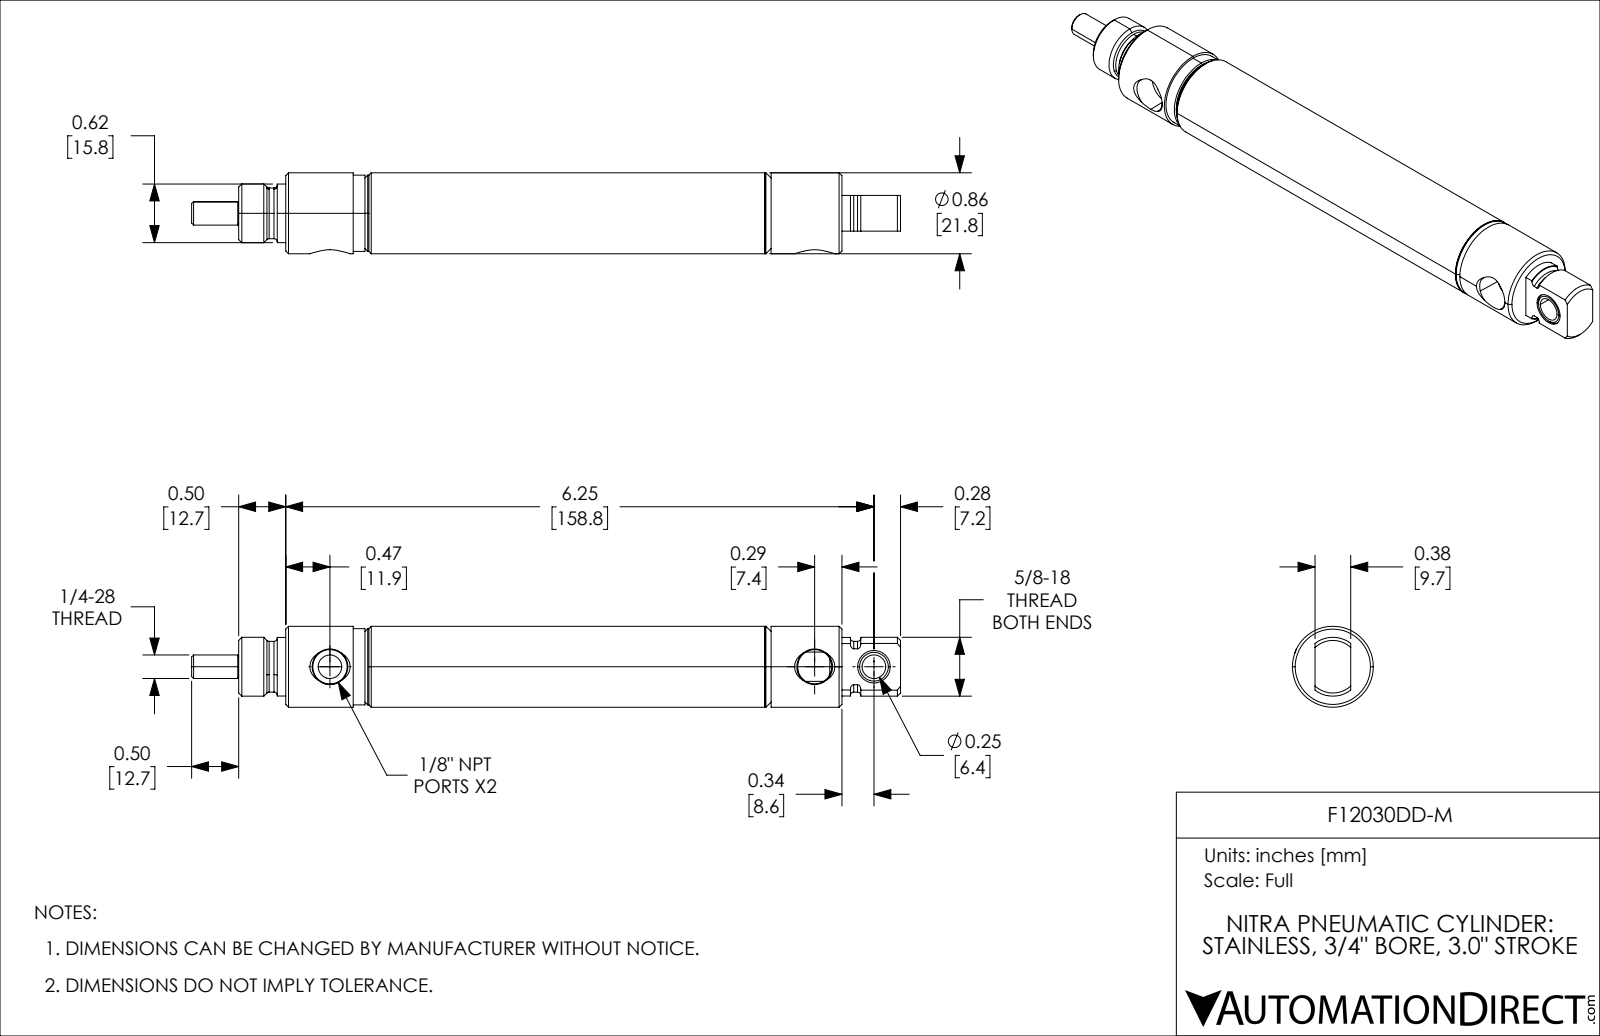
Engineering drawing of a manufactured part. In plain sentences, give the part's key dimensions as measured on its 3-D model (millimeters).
The part is named "F12030DD-M_9; F12030DD-M_11; F12030DD-M_7; F12030DD-M_3 (+2 more)". Its 3-D file was written by "SolidWorks 2021 (CONFIG_CONTROL_DESIGN)". It is 5 solids with 158 faces: 29 planar, 61 cylindrical and 68 other. Overall it measures 191.31 by 21.84 by 21.84 millimeters. Its volume is 37 836 cubic millimeters and its surface area 27 819 square millimeters. Round holes: 1 of diameter 6.35, 1 of diameter 6.38, 1 of diameter 6.95, 1 of diameter 7.92, 1 of diameter 8.78, 1 of diameter 9.23, 1 of diameter 12.7, 1 of diameter 17.83. Round bosses or shafts: 1 of diameter 21.84, 1 of diameter 20.57, 1 of diameter 19.35, 1 of diameter 15.88, 1 of diameter 15.81, 1 of diameter 13.68, 1 of diameter 6.35, 1 of diameter 5.84. Partial cylindrical surfaces (rounded edges, fillets, slot ends): 1 of radius 6.84. The main face-to-face distances are 21.43, 40.49, 138.12, 76.2, 97.63, 122.32, 46.12, 24.69, 12.7, 9.66. The hole center spacings are 16, 130.81, 146.81.
